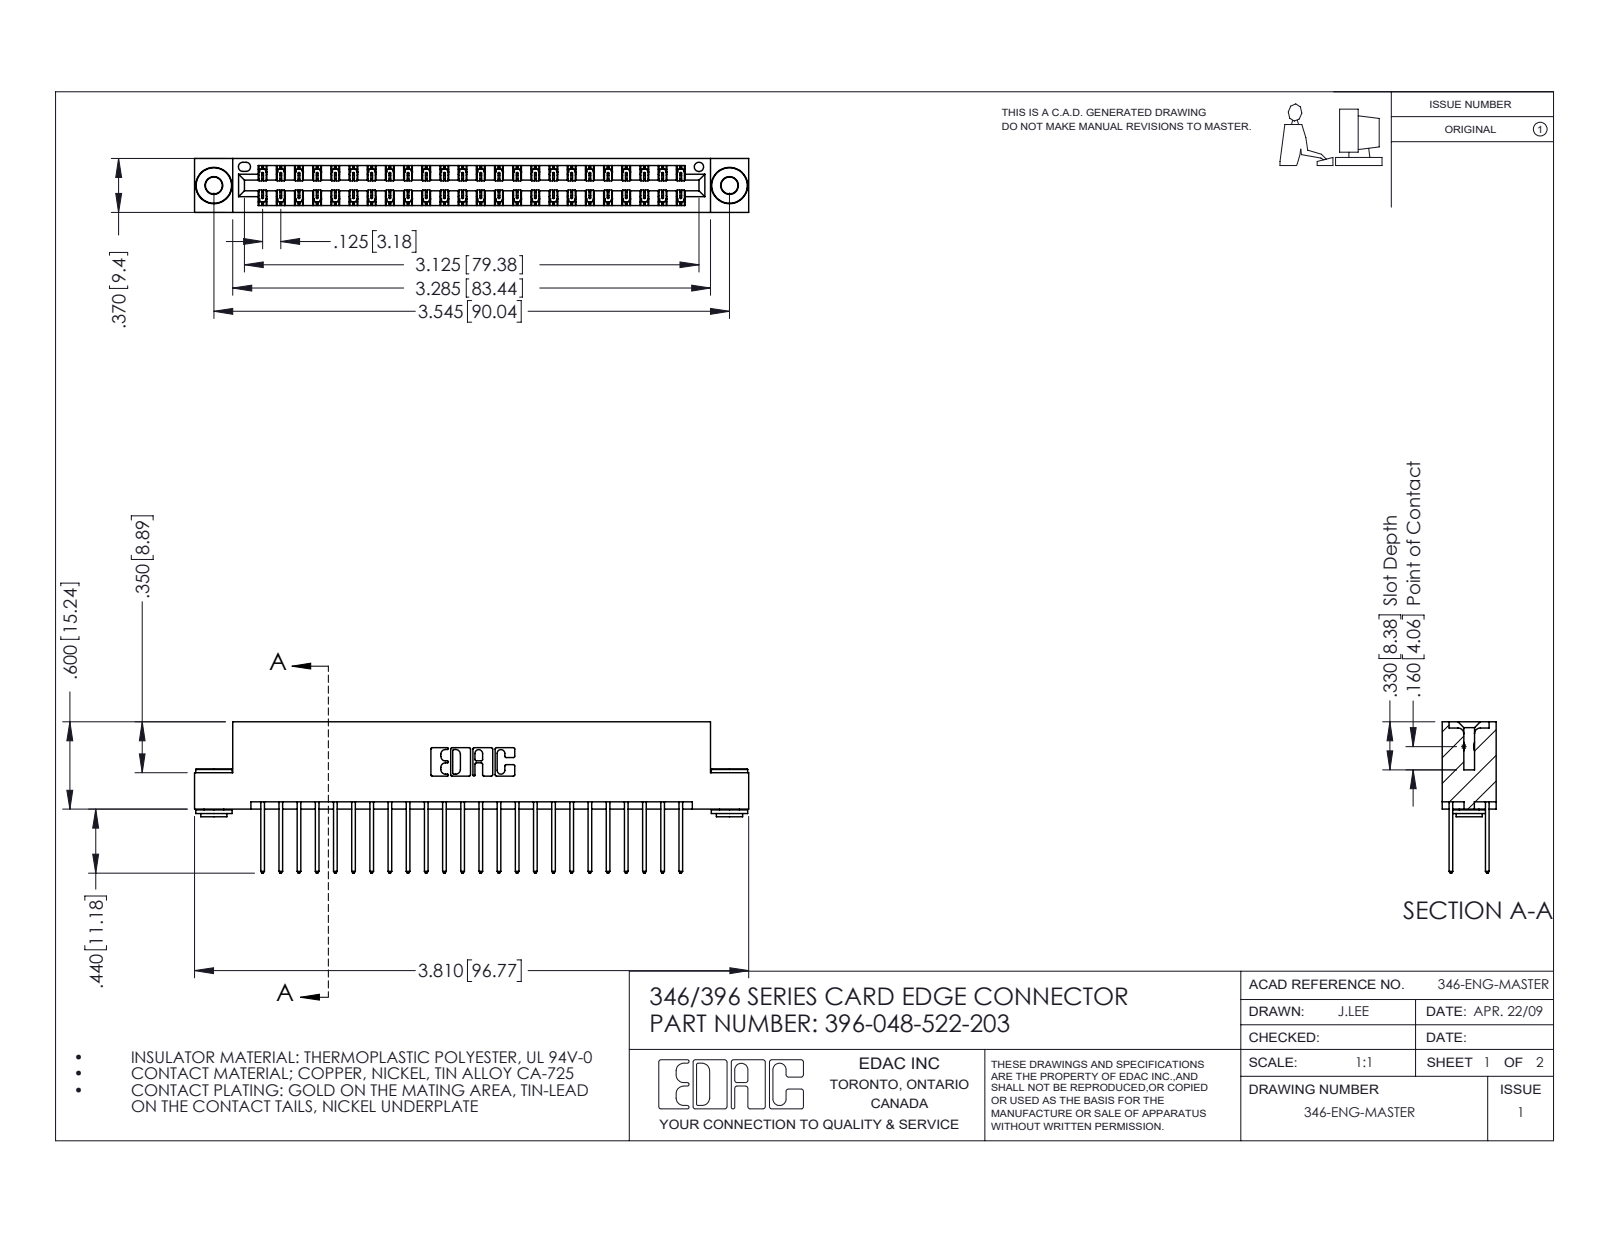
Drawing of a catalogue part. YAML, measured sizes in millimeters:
part_name: "345-292-001_345-293-122; 346 Part_Flush Mounting Lugs - 0.156 Dia-TH; 345-250-002_345-250-002-102; 396-048-522-203"
step_written_by: "SolidWorks 2016 (CONFIG_CONTROL_DESIGN)"
units: millimeters
bodies: {solids: 51, faces: 2656, planar: 1766, cylindrical: 882, other: 8}
overall_size: [96.8, 26.4, 9.4]
volume: 9440
surface_area: 13480
round_holes:
  - {diameter: 2.9, count: 2}
  - {diameter: 4, count: 2}
  - {diameter: 1.6, count: 1}
round_bosses_or_shafts:
  - {diameter: 6.4, count: 2}
  - {diameter: 4.6, count: 2}
  - {diameter: 3.5, count: 2}
partial_cylinders:
  - {radius: 0.2, count: 72}
  - {radius: 0.3, count: 48}
  - {radius: 0.3, count: 22}
  - {radius: 0.2, count: 6}
  - {radius: 0.8, count: 6}
  - {radius: 0.7, count: 3}
  - {radius: 0.4, count: 2}
  - {radius: 0.6, count: 2}
face_to_face_distances: [1.2, 8.2, 6.4, 9.4, 0.6, 1.8, 7.6, 7, 3.8, 5.6]
hole_center_spacings: [6.2, 84.8, 90]
